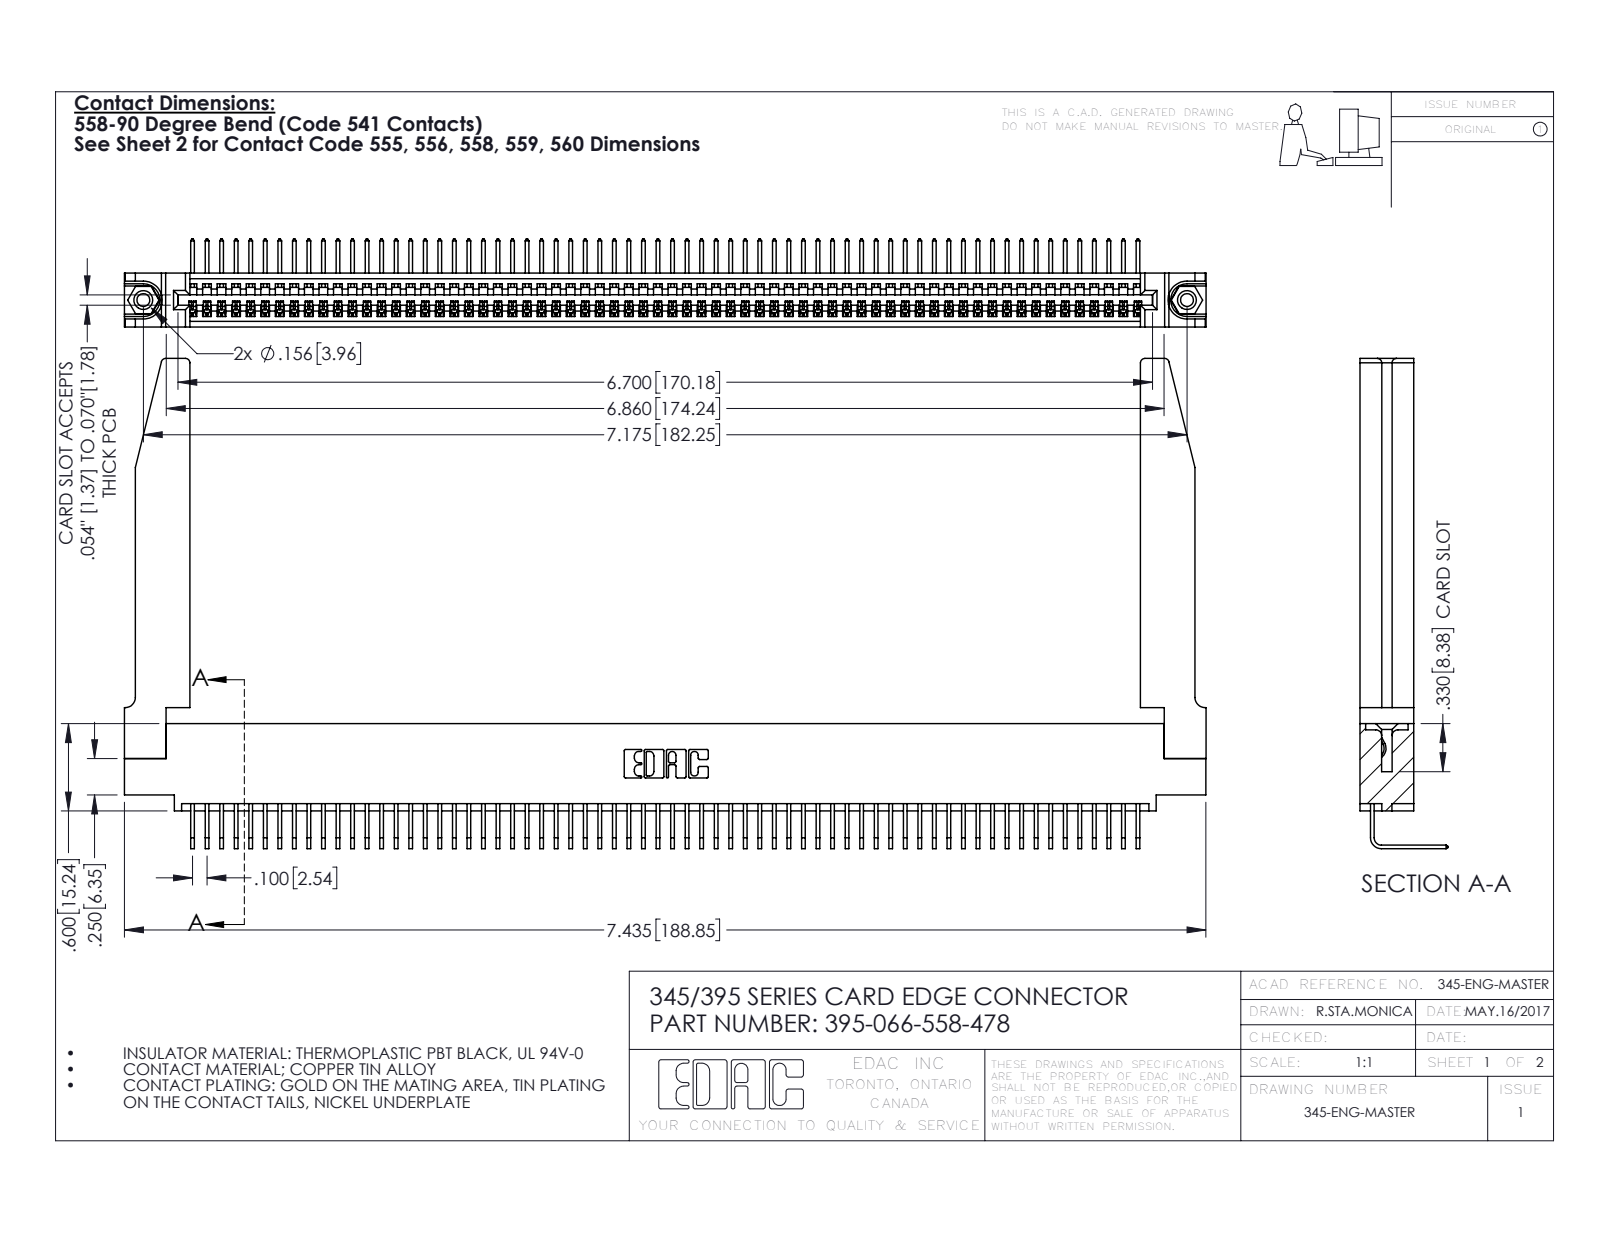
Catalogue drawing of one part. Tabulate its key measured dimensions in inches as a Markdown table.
| quantity | value |
| --- | --- |
| part name | 345 Part_0.110 Offset - 0.156 Dia-TH; 345-250-001_345-250-001-102; 395-066-558-478; 345-220-078_345-220-078 (+1 more) |
| STEP written by | SolidWorks 2016 (CONFIG_CONTROL_DESIGN) |
| units | inches |
| bodies | 71 solids, 4324 faces (2998 planar, 1274 cylindrical, 52 other) |
| overall size | 7.436 × 3.369 × 0.605 |
| volume | 1.59 in³ |
| surface area | 50.9 in² |
| round holes (diameter × count) | 0.089 × 2, 0.125 × 2, 0.156 × 2, 0.064 × 1 |
| round bosses / shafts (diameter × count) | 0.155 × 2 |
| partial cylindrical surfaces (radius × count) | 0.006 × 132, 0.01 × 22, 0.03 × 8, 0.007 × 6, 0.031 × 6, 0.026 × 3, 0.031 × 2, 0.04 × 2 |
| main face-to-face distances | 0.072, 0.37, 0.298, 0.098, 0.272, 0.025, 0.2, 0.225, 0.15, 0.148 |
| hole center spacings | 0.27, 6.939, 7.175 |
